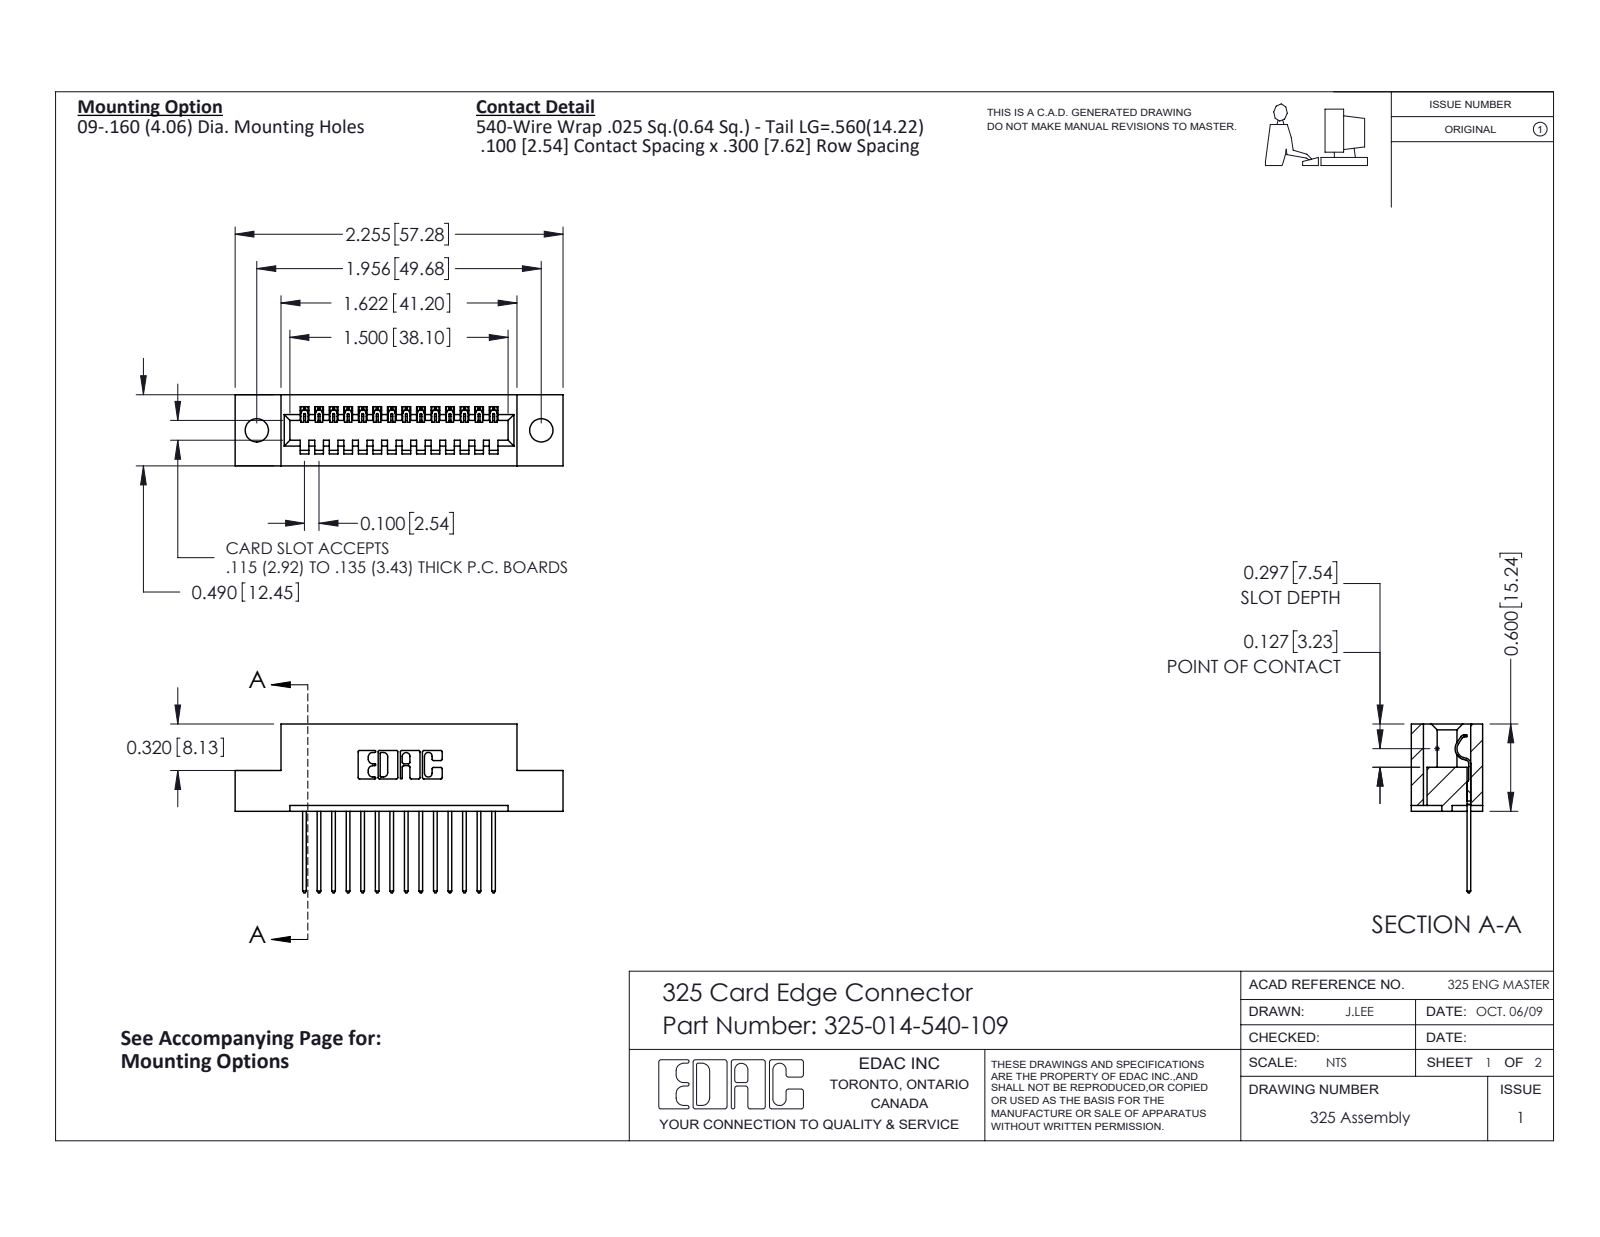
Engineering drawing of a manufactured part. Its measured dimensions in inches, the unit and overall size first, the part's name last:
Units: inches
Overall size (bounding box): 2.255 × 1.16 × 0.49
Round holes (diameter × count): ⌀0.16 ×2
Partial cylindrical surfaces — rounded edges, fillets, slot ends (radius × count): R0.006 ×28, R0.01 ×28, R0.01 ×22, R0.007 ×6, R0.031 ×6, R0.026 ×3, R0.014 ×1, R0.022 ×1
Main face-to-face distances: 0.083, 0.407, 0.3, 0.49, 0.04, 0.107, 0.383, 0.025, 0.1, 0.6
Hole centre spacings: 1.956
Volume: 0.417 in³ · Surface area: 10.9 in²
Bodies: 15 solids, 926 faces (658 planar, 268 cylindrical, 0 other)
Part name (STEP PRODUCT): 325-292-001_325-293-140; 325 Part_.160 TH; 325-014-540-109
STEP written by: SolidWorks 2016 (CONFIG_CONTROL_DESIGN)
